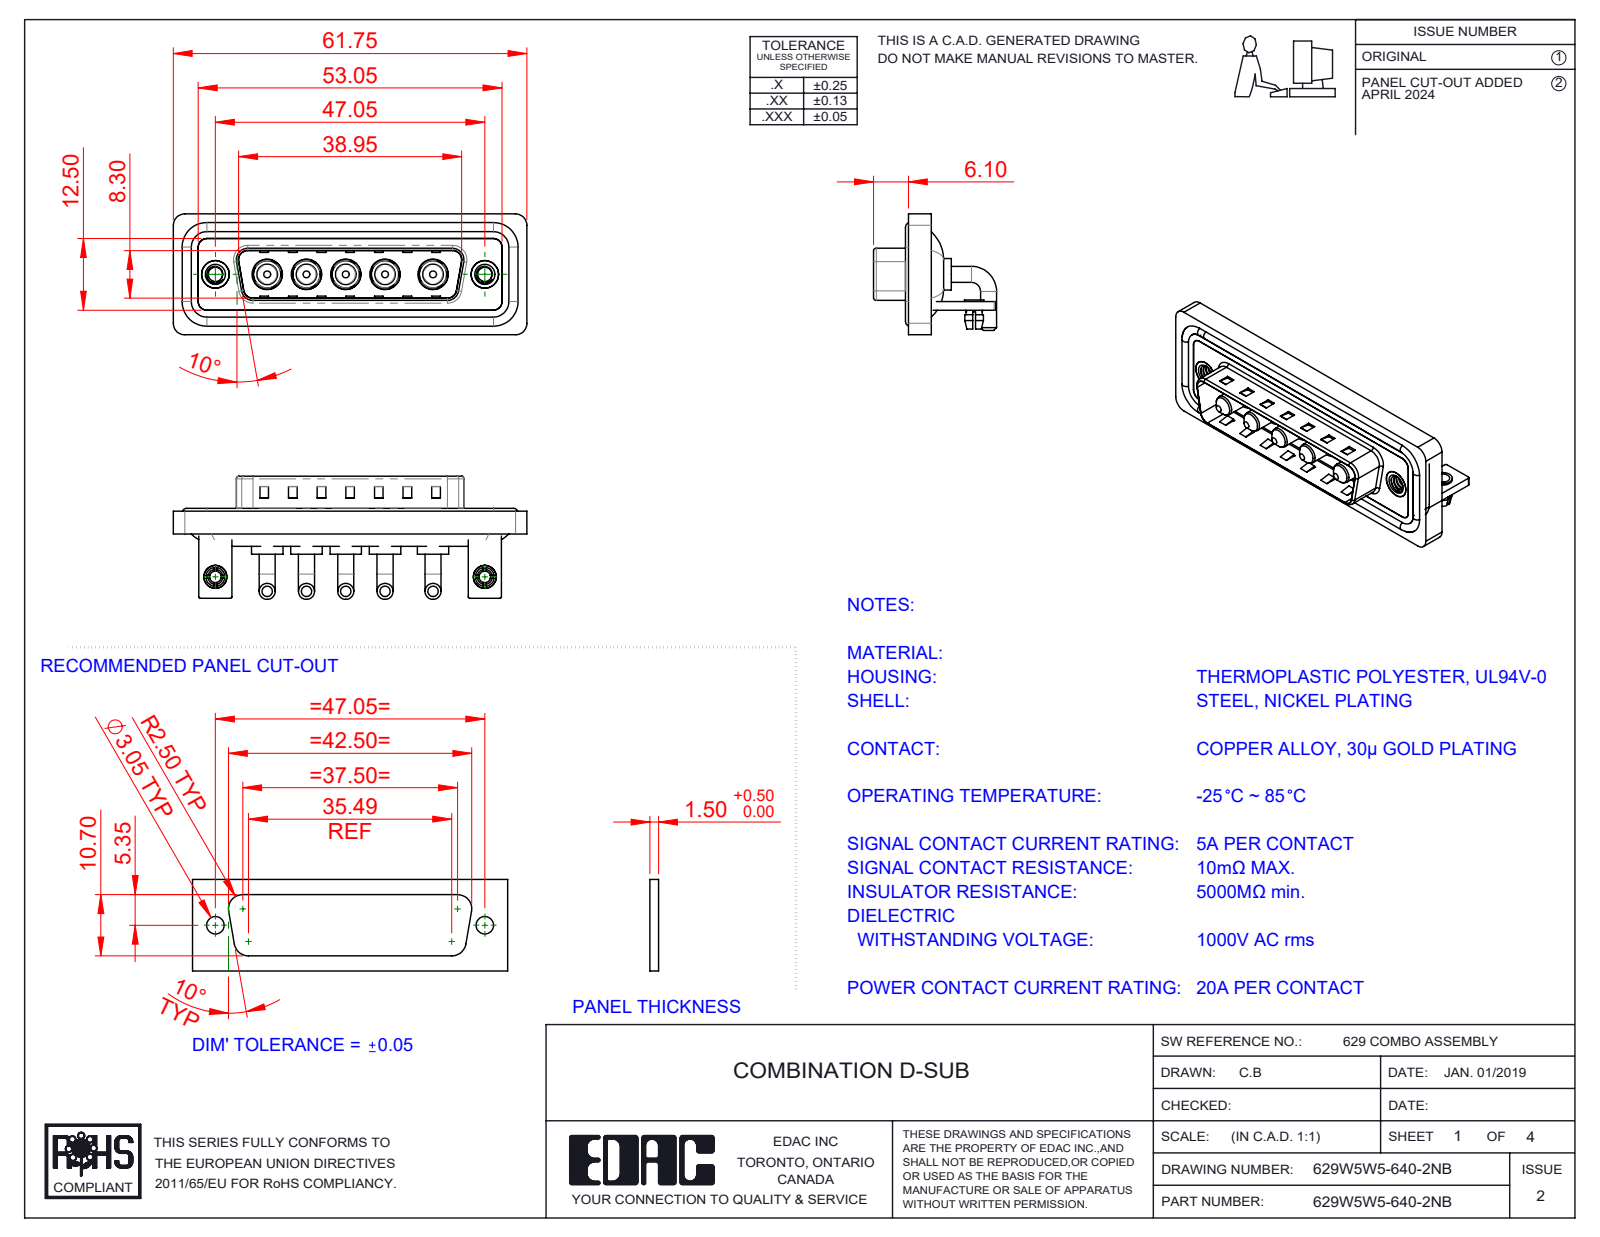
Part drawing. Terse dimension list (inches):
name: Power Pin_20A RA; 629Combo Waterproof Housing_25 Contacts; 629Combo Board Lock; 629Combo Shell Front_25 Contacts (+5 more)
written by: SolidWorks 2023 (CONFIG_CONTROL_DESIGN)
unit: in
bodies: 21 solids, 828 faces (327 planar, 343 cylindrical, 158 other)
size: 2.431 × 0.846 × 0.831
volume: 0.495 in³; area: 20.26 in²
holes: 5× ⌀0.191, 5× ⌀0.209, 4× ⌀0.098, 2× ⌀0.079, 2× ⌀0.126, 2× ⌀0.157, 2× ⌀0.189, 2× ⌀0.197
bosses: 10× ⌀0.11, 5× ⌀0.217, 5× ⌀0.205, 5× ⌀0.187, 5× ⌀0.148, 5× ⌀0.142, 4× ⌀0.063, 2× ⌀0.193
rounds: 19× R0.079, 18× R0.059, 16× R0.01, 9× R0.02, 8× R0.063, 5× R0.083, 4× R0.024, 4× R0.026
face distances: 0.016, 0.059, 0.114, 0.031, 0.083, 0.146, 0.043, 0.177, 0.161, 0.047
hole spacings: 0.27, 0.541, 1.852, 0.27, 0.27, 0.33, 0.33, 0.356
